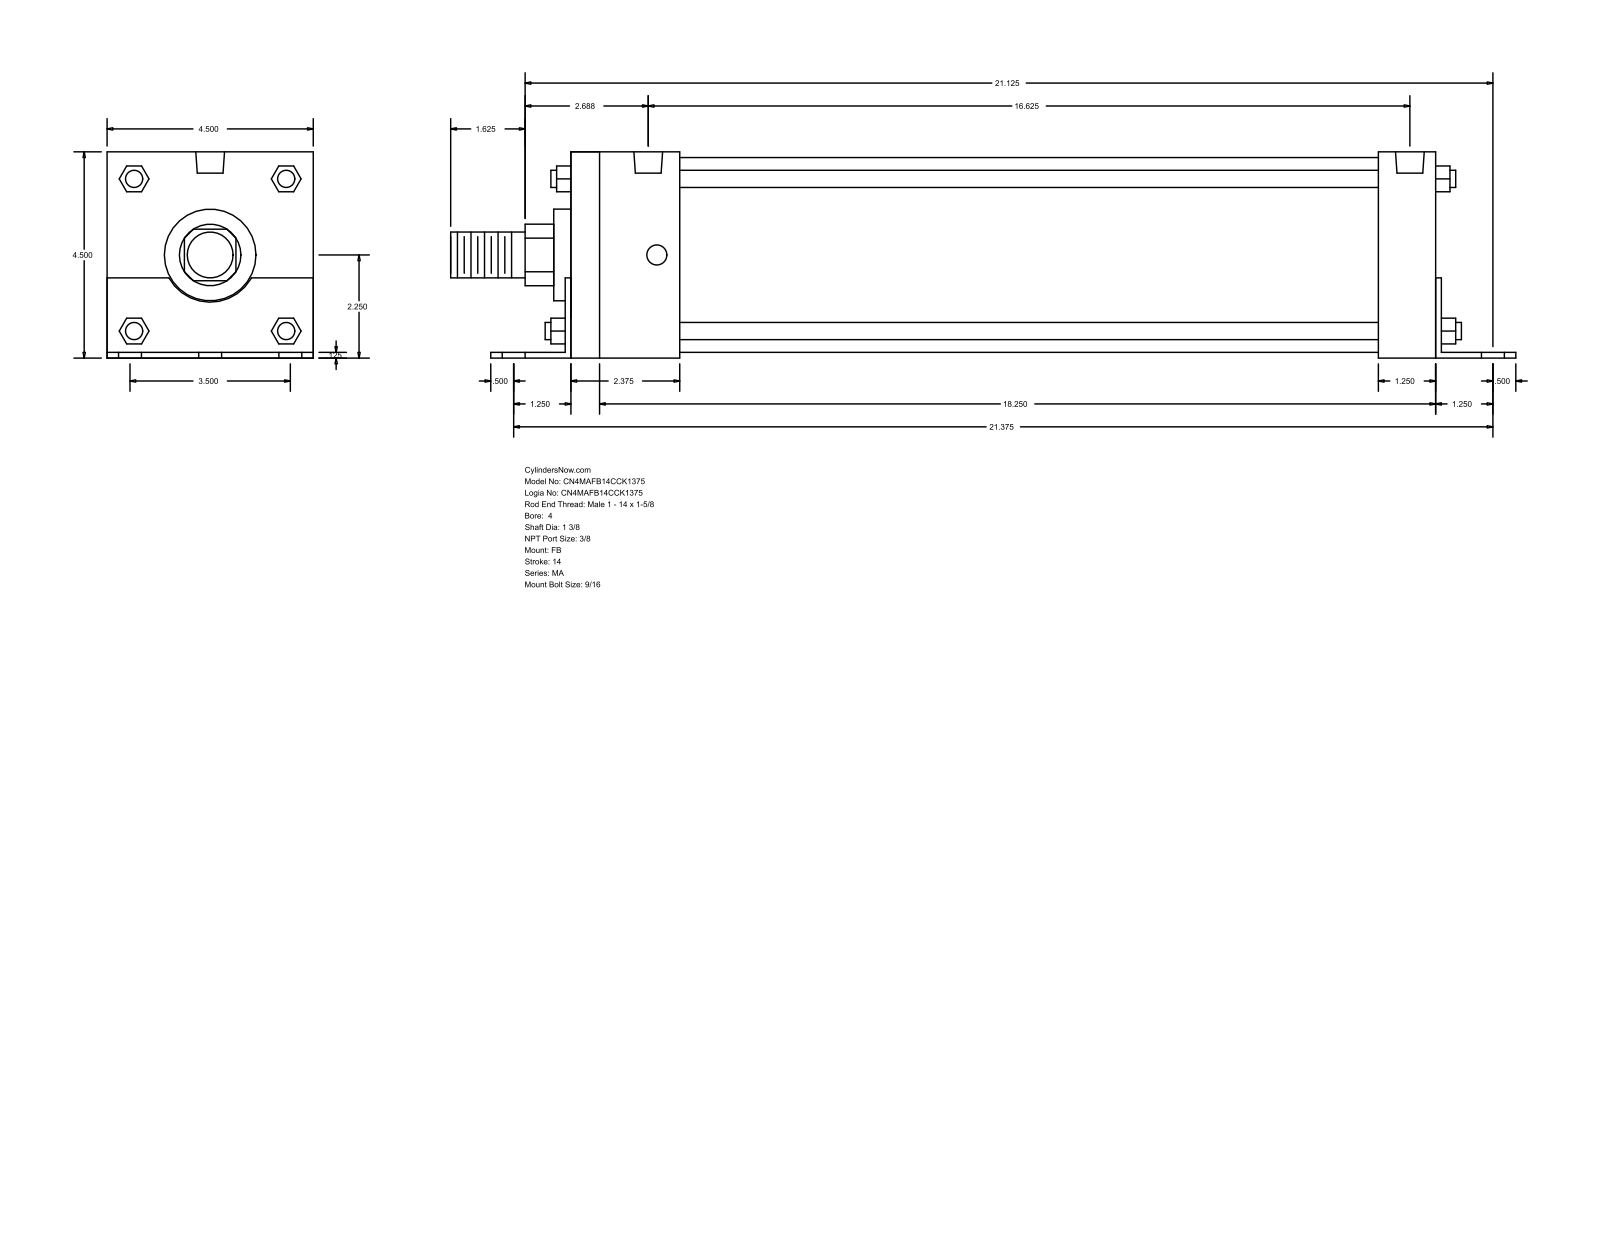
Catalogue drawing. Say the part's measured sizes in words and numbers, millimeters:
The part is named "MA_FB__0400_1.375". Its 3-D file was written by "GSSL Pune (CONFIG_CONTROL_DESIGN)". It is 0 solids with 140 faces: 105 planar, 35 cylindrical and 0 other. Overall it measures 590.55 by 114.35 by 114.3 millimeters. Round holes: 6 of diameter 14.29, 4 of diameter 11.11, 2 of diameter 15.93. Round bosses or shafts: 4 of diameter 9.53, 1 of diameter 107.95, 1 of diameter 50.8, 1 of diameter 34.92, 1 of diameter 25.4. Partial cylindrical surfaces (rounded edges, fillets, slot ends): 1 of radius 17.06, 1 of radius 26.16. The main face-to-face distances are 114.3, 3.17, 114.35, 3.12, 111.18, 479.42, 3.18, 482.6, 34.93, 482.59. The hole center spacings are 44.45, 544.75, 542.93, 4.77, 64, 67.51, 86.85, 88.9.
